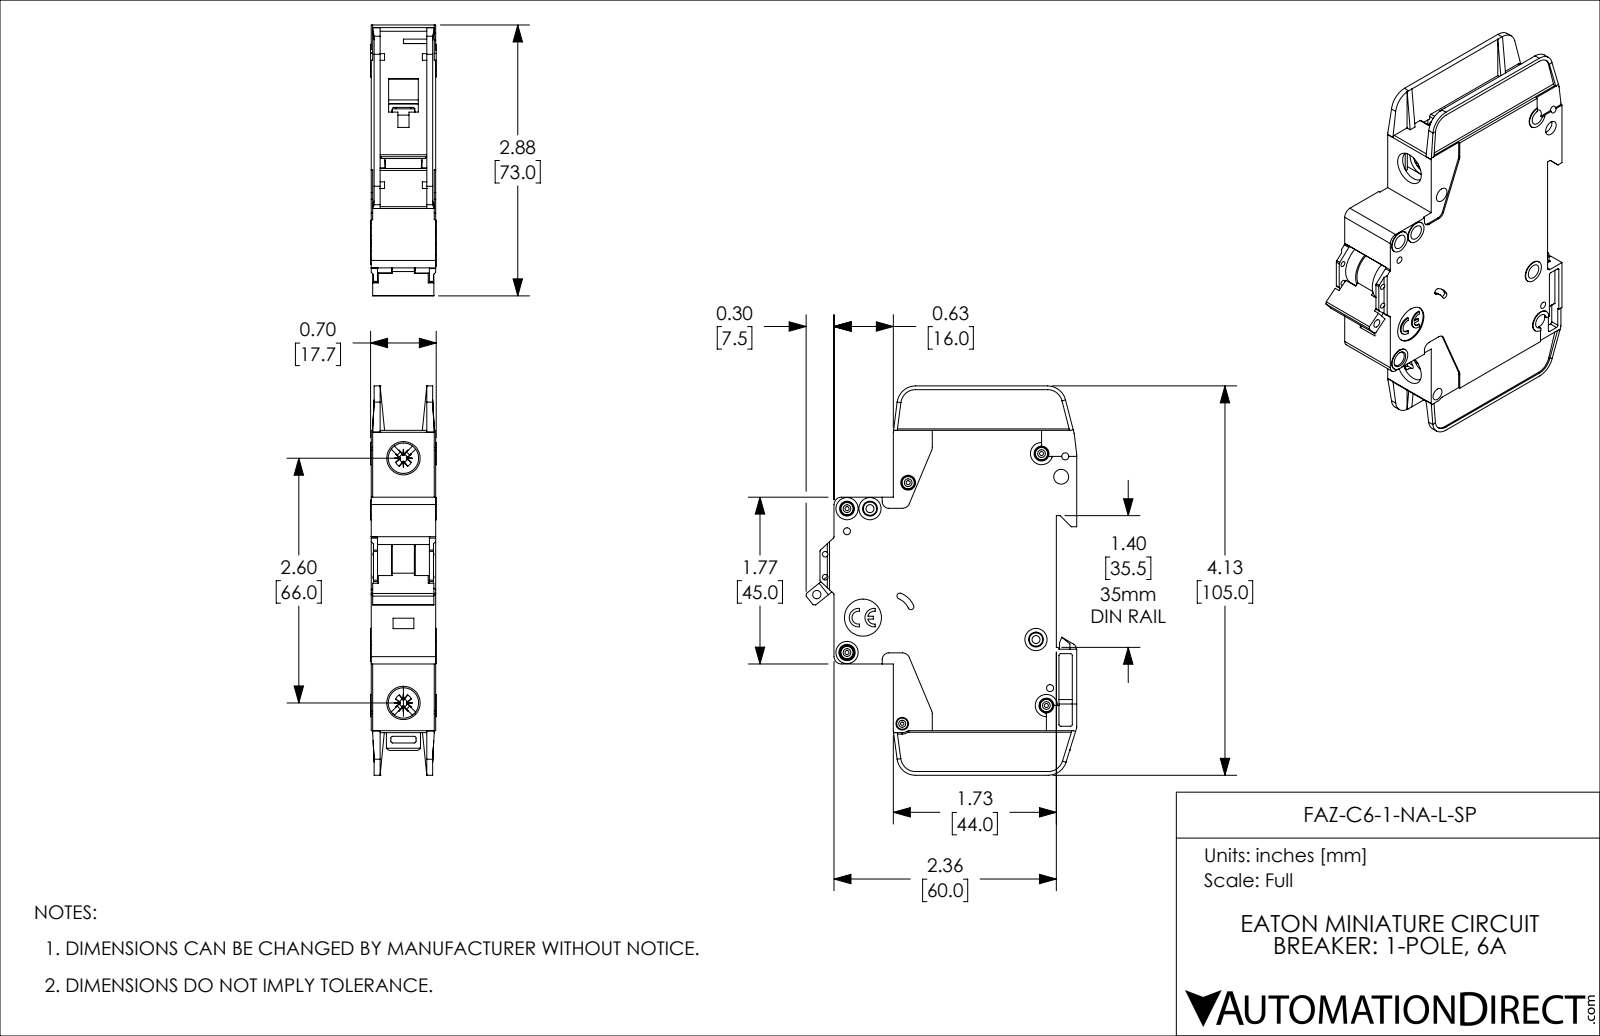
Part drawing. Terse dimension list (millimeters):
name: FAZ-C6-1-NA-L-SP
written by: SolidWorks 2019 (AUTOMOTIVE_DESIGN)
unit: mm
bodies: 1 solid, 1127 faces (671 planar, 357 cylindrical, 99 other)
size: 105 × 73.1 × 17.7
volume: 76 720 mm³; area: 26 460 mm²
holes: 8× ⌀4, 5× ⌀1.1, 4× ⌀1.9, 2× ⌀1.5, 2× ⌀2.2, 2× ⌀8.2, 1× ⌀0.9, 1× ⌀2.3, 1× ⌀2.5, 1× ⌀3.4, 1× ⌀10
bosses: 5× ⌀3.3, 4× ⌀6, 2× ⌀3, 1× ⌀2.5
rounds: 42× R0.5, 10× R0.4, 10× R1, 8× R2, 5× R5, 4× R0.2, 4× R0.7, 4× R1.1
face distances: 1.2, 17.4, 15, 16.2, 2.4, 13.8, 0.4, 0.8, 12.6, 14.6
hole spacings: 6.2, 13.6, 22.1, 4.8, 5.1, 5.2, 5.6, 6.1
